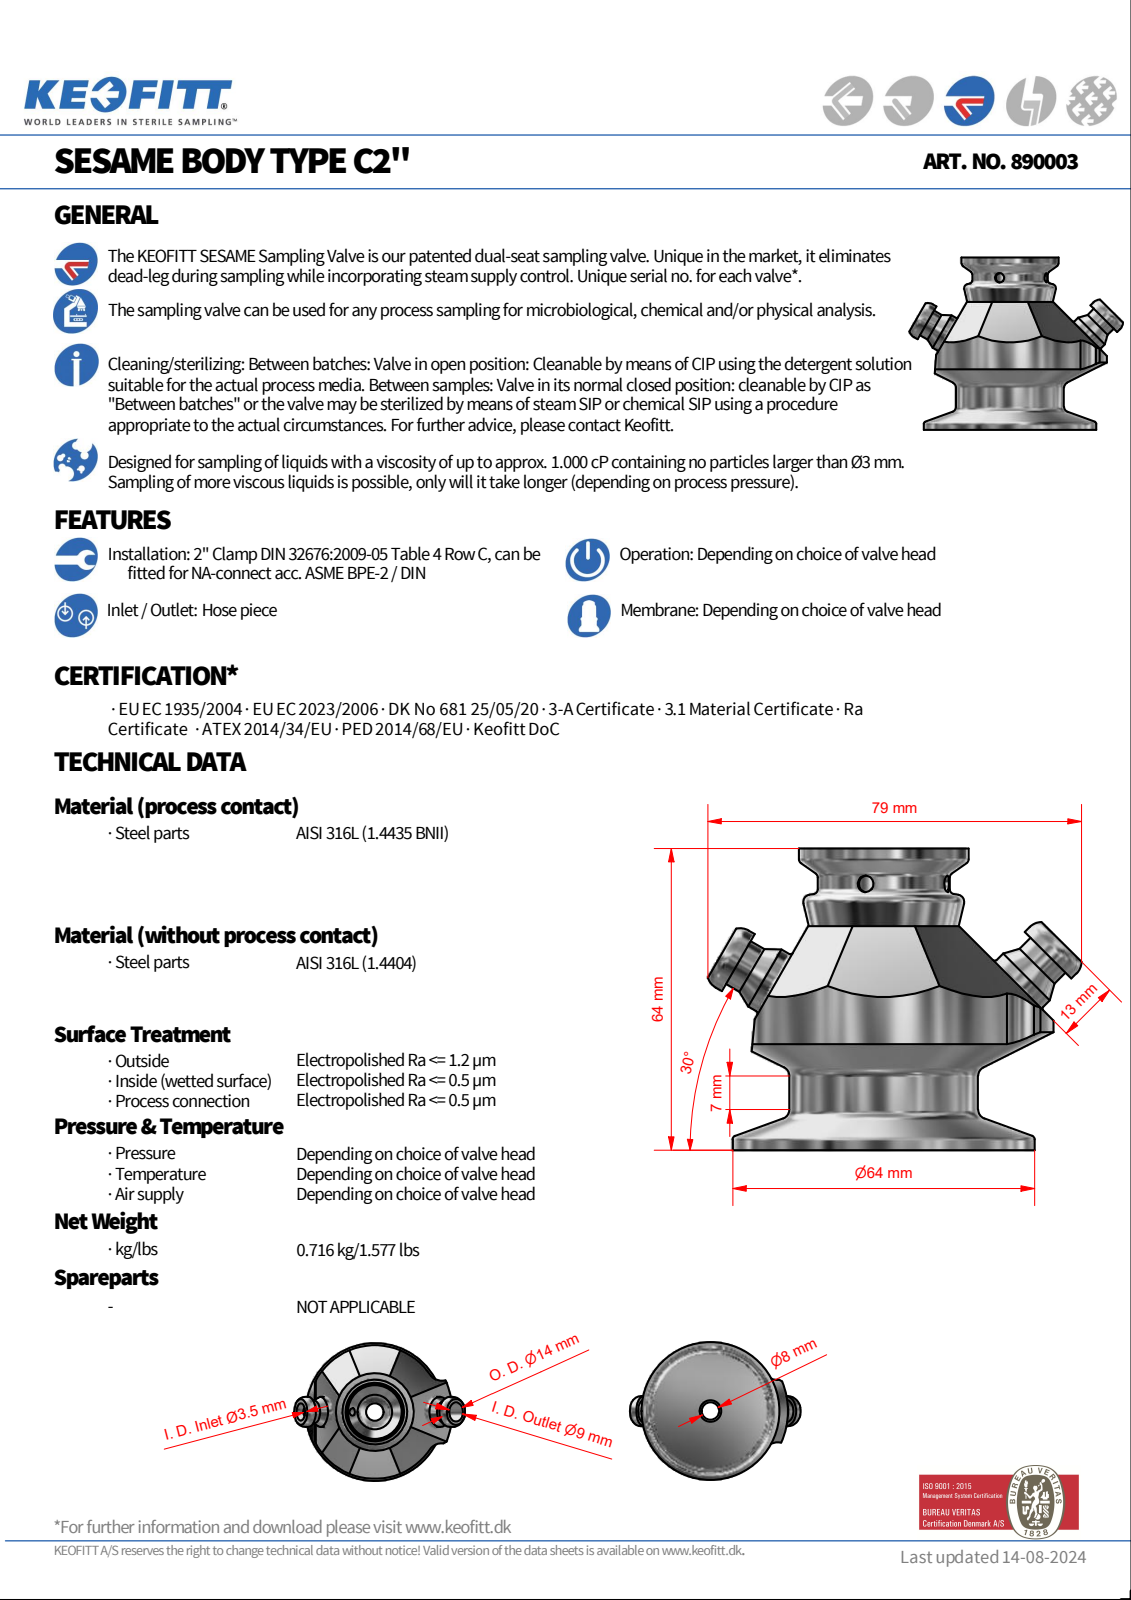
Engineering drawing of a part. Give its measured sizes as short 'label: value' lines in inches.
name: 890003
written by: Autodesk Inventor 2017 (AUTOMOTIVE_DESIGN)
unit: in
bodies: 1 solid, 87 faces (23 planar, 37 cylindrical, 27 other)
size: 3.119 × 2.52 × 2.52
volume: 6.82 in³; area: 32.92 in²
holes: 3× ⌀0.138, 1× ⌀0.354, 1× ⌀1.142, 1× ⌀1.181
bosses: 2× ⌀0.551, 2× ⌀0.413, 1× ⌀2.52, 1× ⌀1.575, 1× ⌀1.417, 1× ⌀1.13, 1× ⌀1.122, 1× ⌀1.102
rounds: 2× R0.276, 1× R1.22, 1× R1.417
face distances: 2.43, 2.52, 0.09, 2.402, 0.028, 0.118, 1.87, 0.531, 0.56, 0.65
